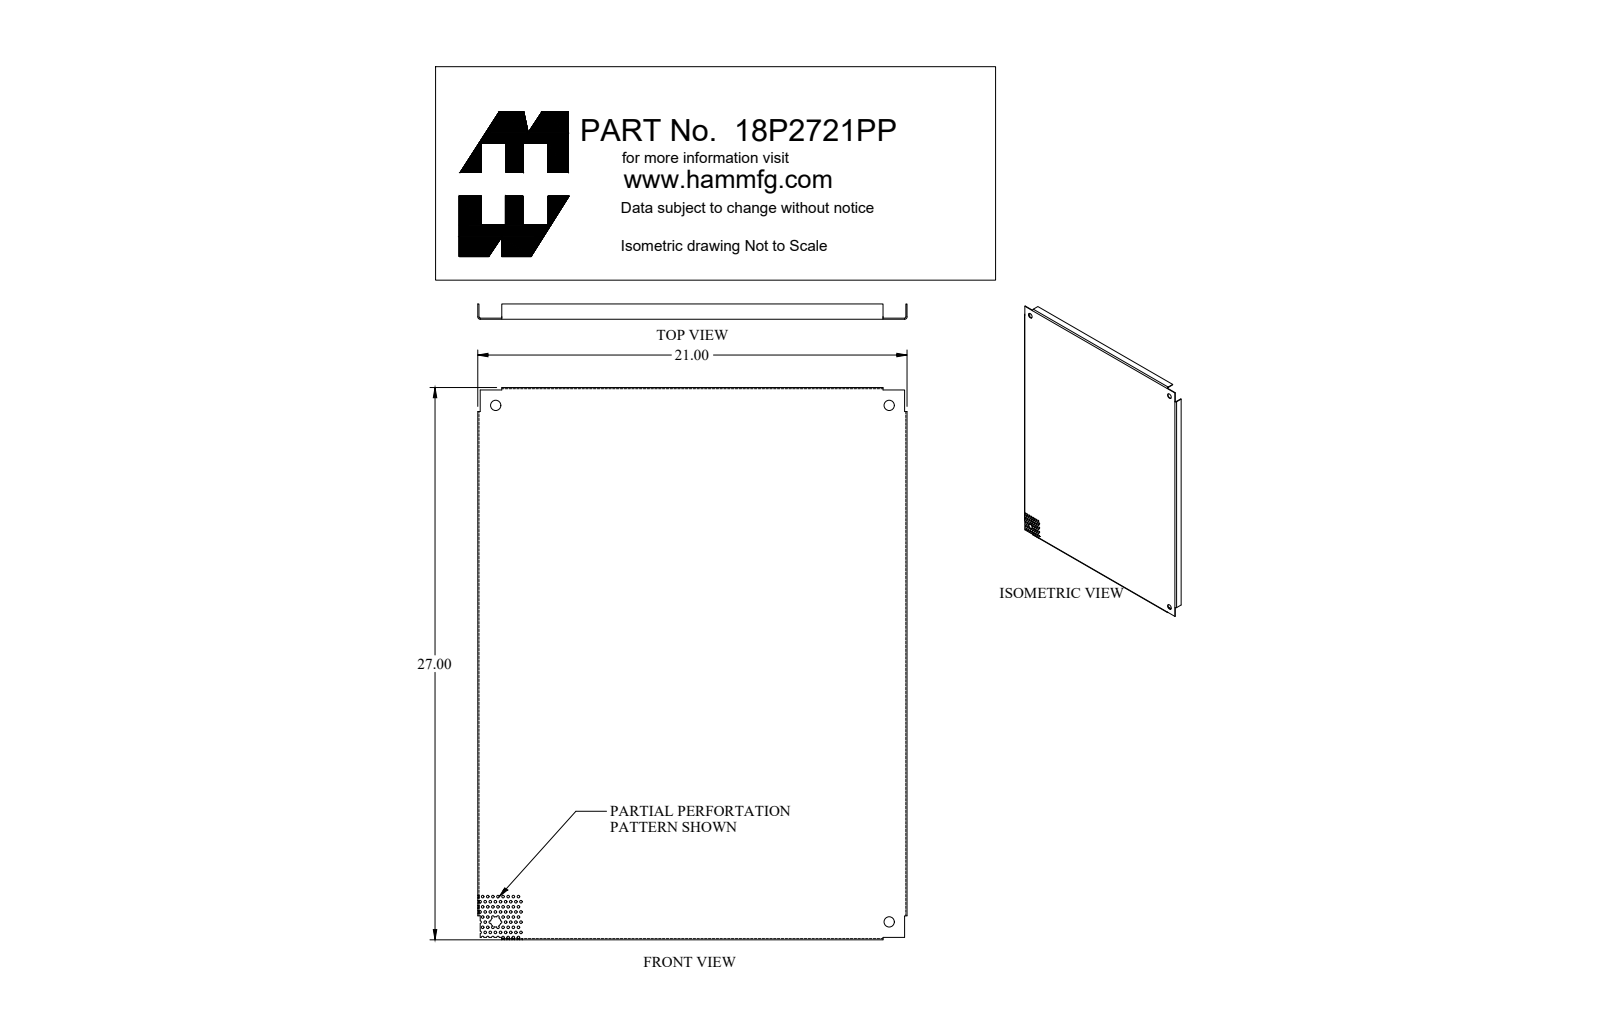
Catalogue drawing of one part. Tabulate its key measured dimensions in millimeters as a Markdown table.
| quantity | value |
| --- | --- |
| part name | 18P2721PP_Default |
| STEP written by | SolidWorks 2018 (CONFIG_CONTROL_DESIGN) |
| units | millimeters |
| bodies | 1 solid, 254 faces (43 planar, 203 cylindrical, 8 other) |
| overall size | 685.8 × 533.4 × 19.1 |
| volume | 581 100 mm³ |
| surface area | 807 700 mm² |
| round holes (diameter × count) | 3.2 × 74, 12.7 × 3 |
| partial cylindrical surfaces (radius × count) | 1.6 × 17, 1.6 × 8, 0.7 × 4, 2.2 × 4, 6.4 × 1 |
| main face-to-face distances | 1.4, 532, 684.4, 530.5, 533.4, 685.8, 682.9, 19.1, 17.6, 2.6 |
| hole center spacings | 7.1, 12.7, 6.4, 14.2, 11.5, 19.3, 18, 19.1 |
